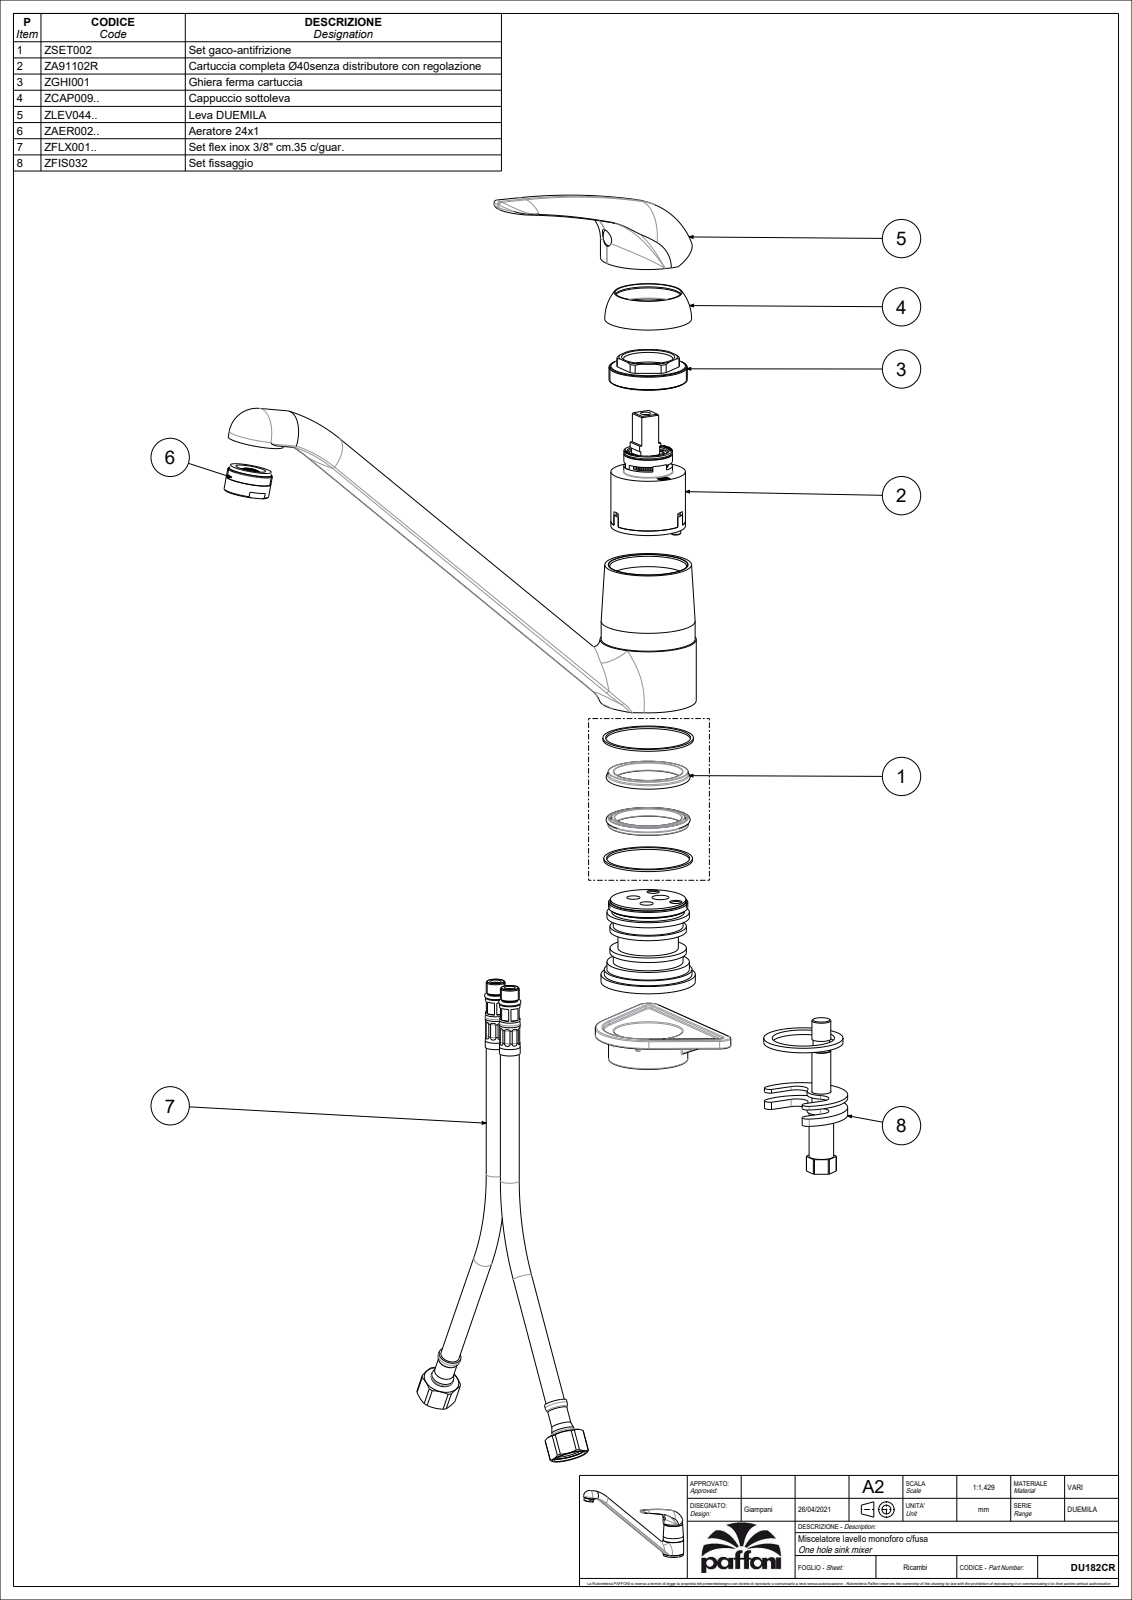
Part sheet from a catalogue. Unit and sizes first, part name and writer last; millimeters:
Units: millimetres
Overall size (bounding box): 280.18 × 196.38 × 51
Round holes (diameter × count): ⌀9.2 ×1, ⌀48.2 ×1
Round bosses / shafts (diameter × count): ⌀51 ×1, ⌀50 ×1, ⌀49.8 ×1, ⌀46.5 ×1, ⌀44.8 ×1, ⌀29.69 ×1, ⌀24 ×1, ⌀18.1 ×1
Partial cylindrical surfaces — rounded edges, fillets, slot ends (radius × count): R1.5 ×2, R14.84 ×2, R15 ×2, R24 ×2, R24.5 ×2, R217.81 ×2, R18 ×1, R39.04 ×1
Main face-to-face distances: 93.4, 37.9, 55.5, 4.4, 33.5, 89, 4, 0.4, 33.9, 89.4
Volume: 332 023 mm³ · Surface area: 55 083 mm²
Bodies: 1 solid, 115 faces (23 planar, 38 cylindrical, 54 other)
Part name (STEP PRODUCT): DU182CR
STEP written by: CREO PARAMETRIC BY PTC INC, 2020044 (CONFIG_CONTROL_DESIGN)
